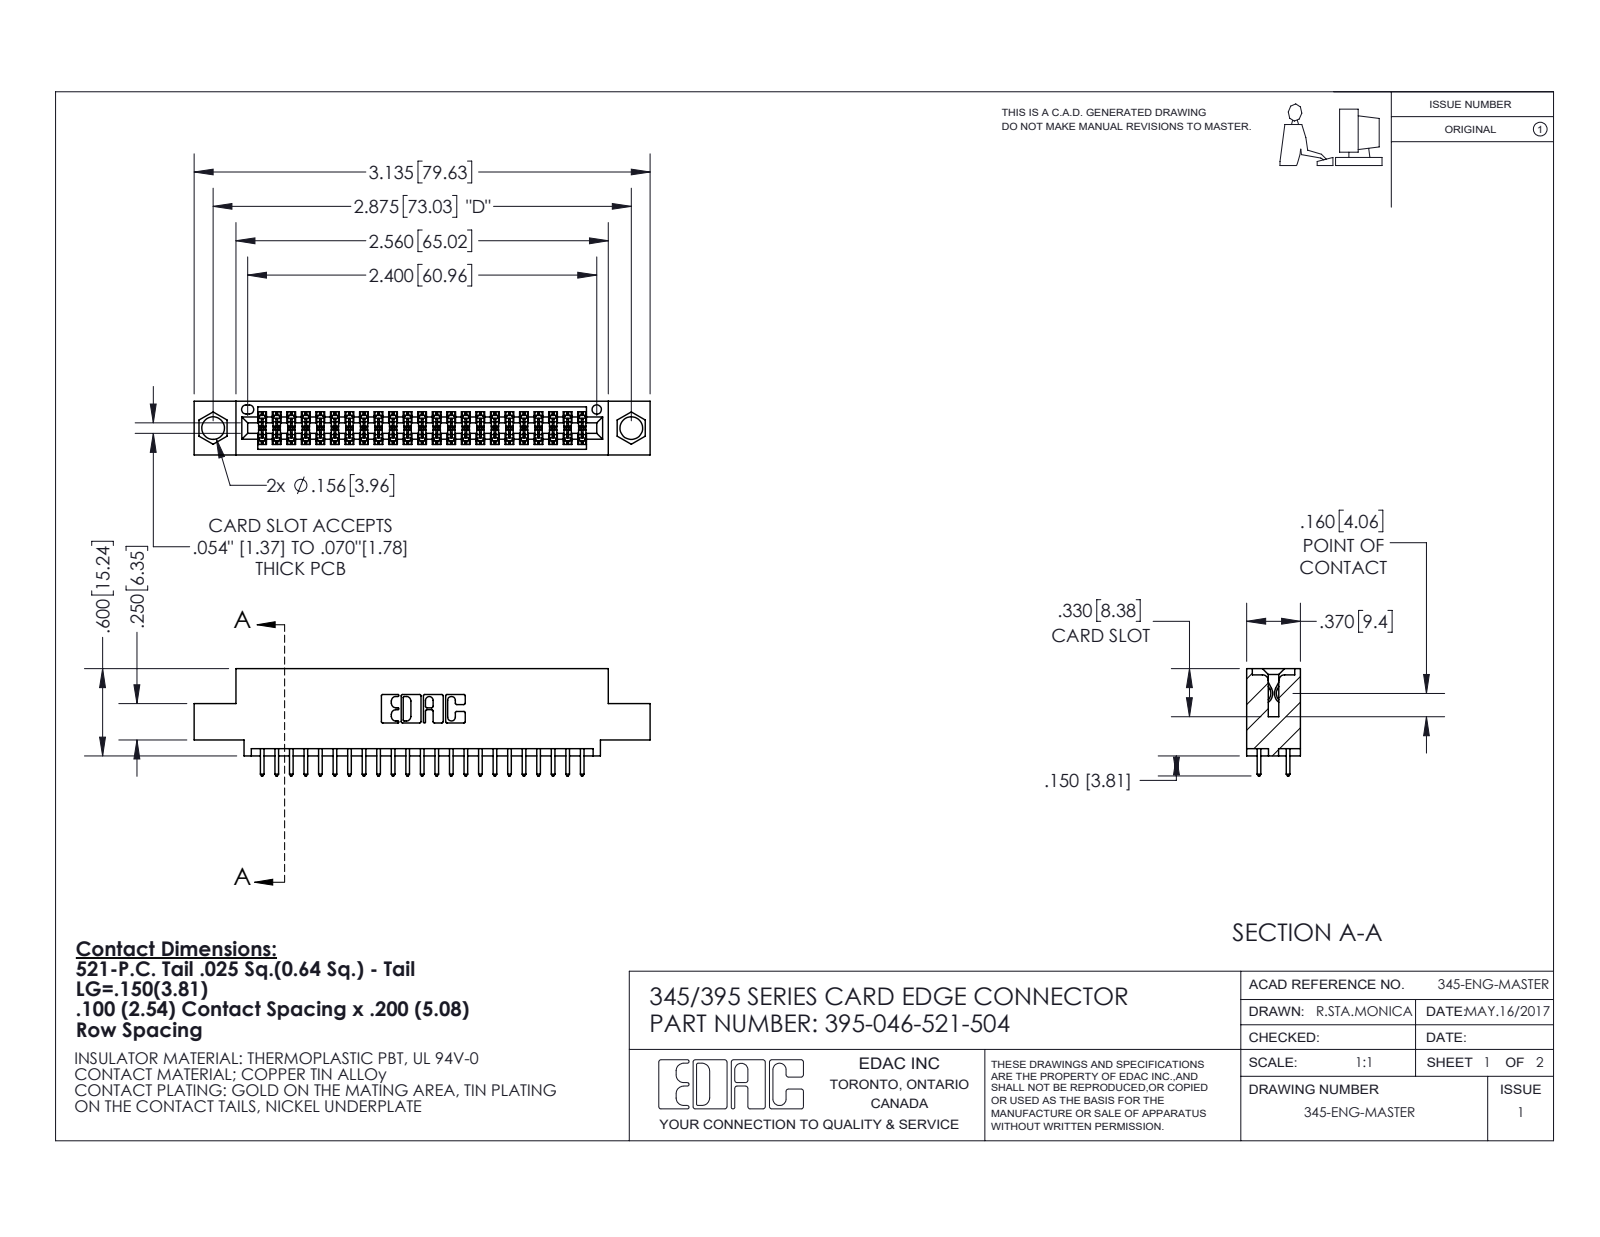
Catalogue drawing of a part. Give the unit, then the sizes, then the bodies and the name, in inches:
Units: inches
Overall size (bounding box): 3.135 × 0.737 × 0.37
Round holes (diameter × count): ⌀0.156 ×2, ⌀0.064 ×1
Partial cylindrical surfaces — rounded edges, fillets, slot ends (radius × count): R0.006 ×69, R0.01 ×46, R0.01 ×22, R0.007 ×6, R0.031 ×6, R0.026 ×3, R0.014 ×2, R0.019 ×2
Main face-to-face distances: 0.298, 0.072, 0.2, 0.37, 0.098, 0.272, 0.025, 0.225, 0.175, 0.149
Hole centre spacings: 0.27, 2.641, 2.875
Volume: 0.449 in³ · Surface area: 16.02 in²
Bodies: 47 solids, 2444 faces (1616 planar, 828 cylindrical, 0 other)
Part name (STEP PRODUCT): 345 Part_0.110 Offset - 0.156 Dia-TI; 395-046-521-504; 345-292-001_345-293-121
STEP written by: SolidWorks 2020 (CONFIG_CONTROL_DESIGN)
